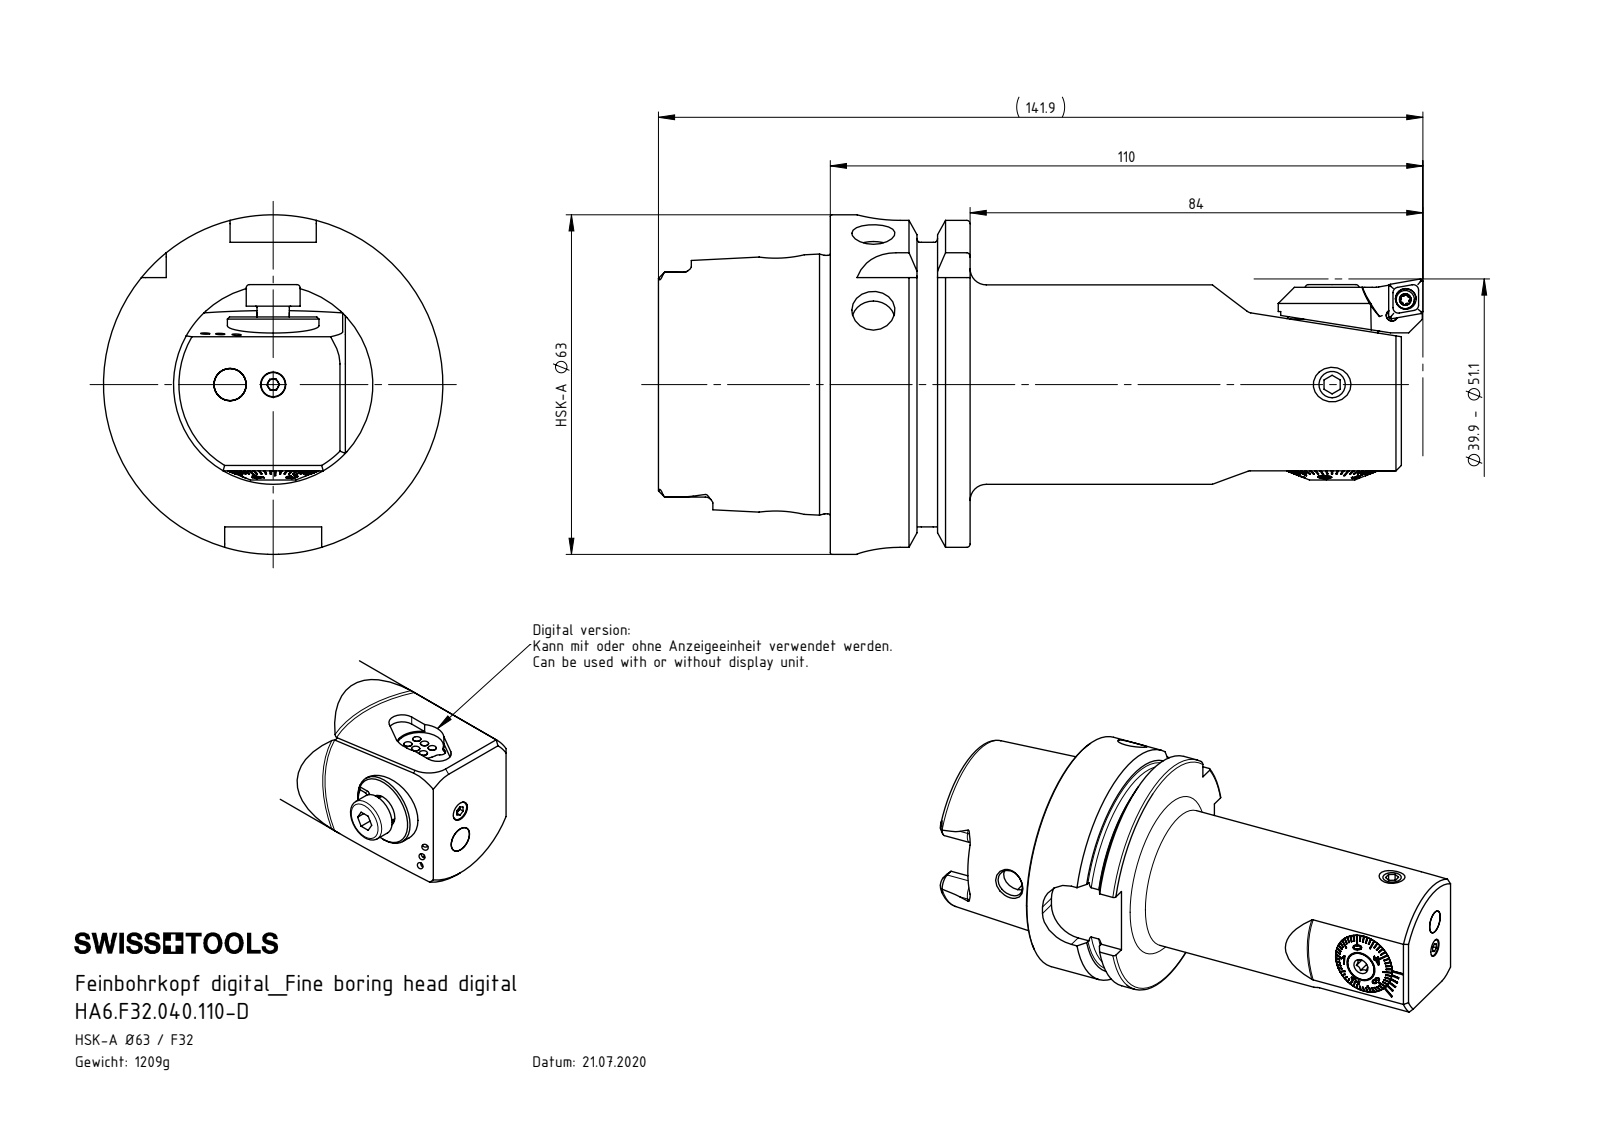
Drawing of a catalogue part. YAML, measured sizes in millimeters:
part_name: "F32-BG2.017.003_A; F32-BG2.014.012_A; F32-BG1.DA4.017_Standart; F32-BG2.009.012_A (+8 more)"
step_written_by: "SolidWorks 2022 (CONFIG_CONTROL_DESIGN)"
units: millimeters
bodies: {solids: 15, faces: 937, planar: 449, cylindrical: 185, other: 303}
overall_size: [137.9, 63, 63]
volume: 154954
surface_area: 41466
round_holes:
  - {diameter: 1.5, count: 3}
  - {diameter: 3.3, count: 2}
  - {diameter: 5, count: 2}
  - {diameter: 8, count: 2}
  - {diameter: 8.5, count: 2}
  - {diameter: 2.05, count: 1}
  - {diameter: 2.7, count: 1}
  - {diameter: 2.9, count: 1}
  - {diameter: 3, count: 1}
  - {diameter: 4.2, count: 1}
  - {diameter: 6, count: 1}
  - {diameter: 7, count: 1}
round_bosses_or_shafts:
  - {diameter: 1.9, count: 6}
  - {diameter: 6, count: 2}
  - {diameter: 63, count: 1}
  - {diameter: 54.95, count: 1}
  - {diameter: 47.94, count: 1}
  - {diameter: 37, count: 1}
  - {diameter: 17, count: 1}
  - {diameter: 16.98, count: 1}
partial_cylinders:
  - {radius: 1.4, count: 10}
  - {radius: 2.88, count: 4}
  - {radius: 8, count: 4}
  - {radius: 0.5, count: 3}
  - {radius: 1.1, count: 3}
  - {radius: 1.2, count: 3}
  - {radius: 1.75, count: 2}
  - {radius: 2, count: 2}
face_to_face_distances: [25.95, 106, 80.05, 16, 9.95, 96.05, 31.9, 4.5, 41.85, 57.85]
hole_center_spacings: [1.52, 8, 8.72, 10.24, 85.04, 86.15, 93.16, 102.15]
